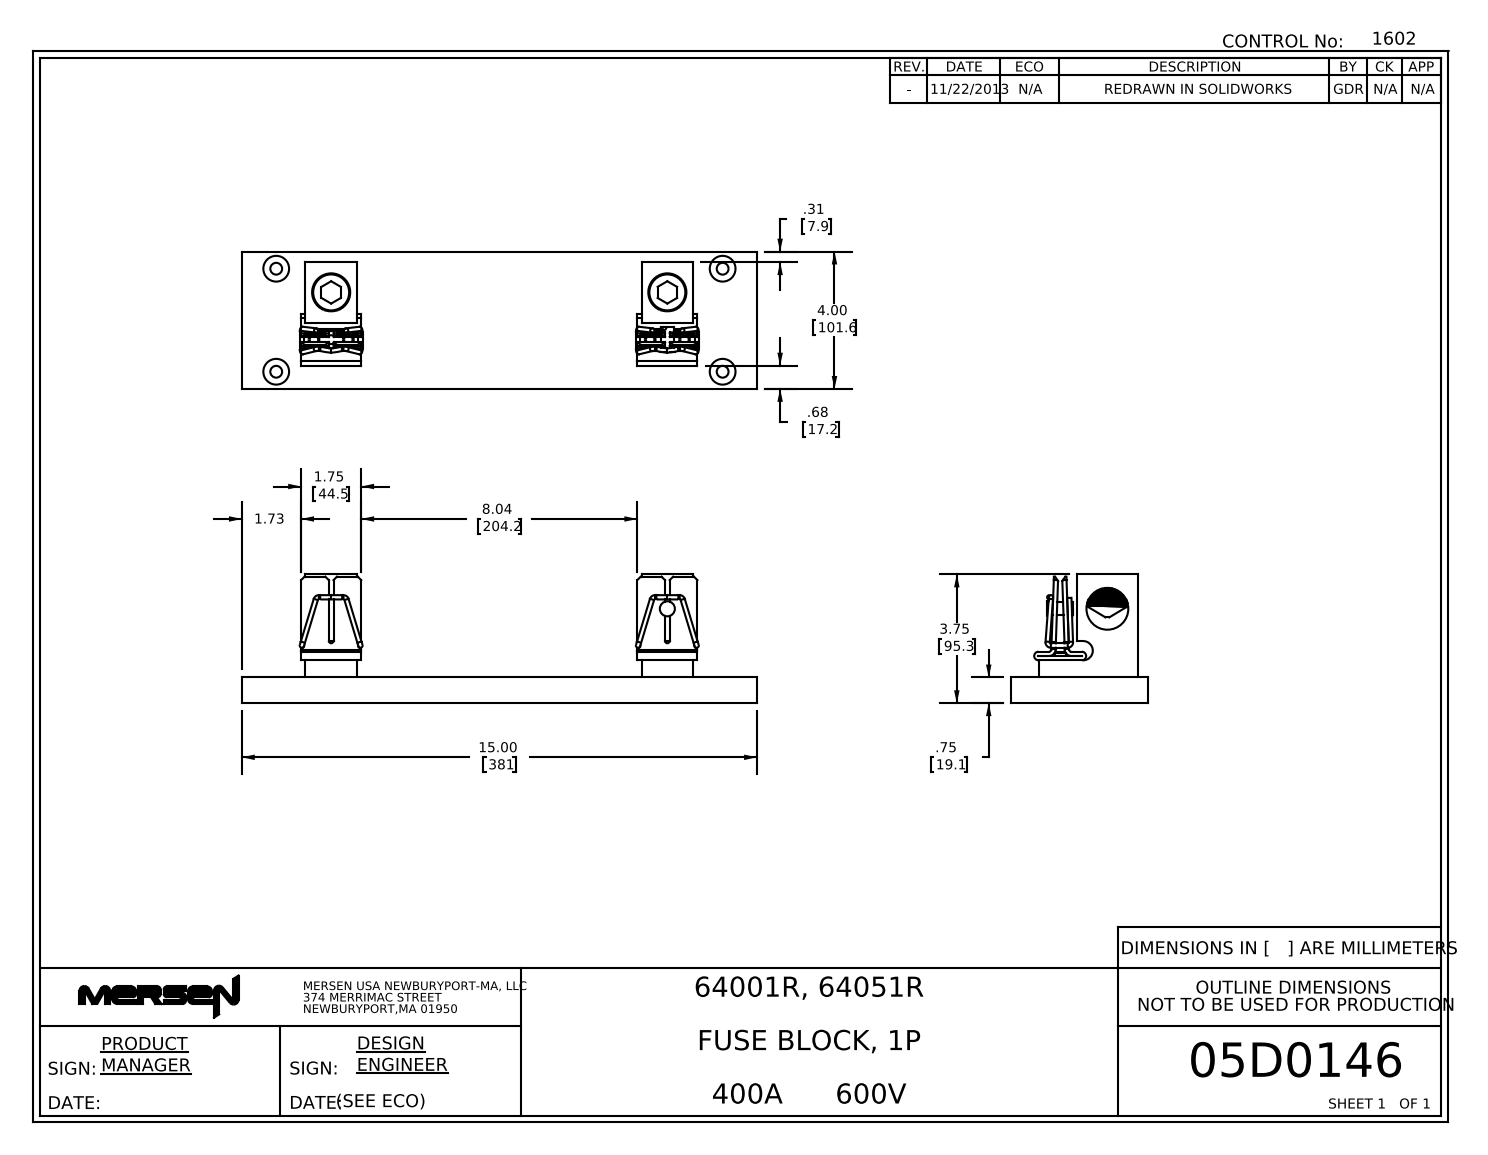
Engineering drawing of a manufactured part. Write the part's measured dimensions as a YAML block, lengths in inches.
part_name: "05D0146rev"
step_written_by: "SolidWorks 2013 (AUTOMOTIVE_DESIGN)"
units: inches
bodies: {solids: 18, faces: 511, planar: 214, cylindrical: 142, other: 155}
overall_size: [15, 4, 3.75]
volume: 60.58
surface_area: 319.6
round_holes:
  - {diameter: 0.257, count: 4}
  - {diameter: 0.266, count: 4}
  - {diameter: 0.339, count: 4}
  - {diameter: 0.344, count: 4}
  - {diameter: 0.377, count: 4}
  - {diameter: 0.625, count: 4}
  - {diameter: 0.75, count: 4}
  - {diameter: 0.85, count: 4}
  - {diameter: 1.047, count: 2}
  - {diameter: 1.218, count: 2}
round_bosses_or_shafts:
  - {diameter: 1.095, count: 28}
  - {diameter: 0.313, count: 8}
  - {diameter: 1.17, count: 2}
  - {diameter: 0.438, count: 1}
  - {diameter: 0.375, count: 1}
partial_cylinders:
  - {radius: 0.094, count: 4}
  - {radius: 0.125, count: 3}
  - {radius: 0.063, count: 2}
  - {radius: 0.069, count: 2}
  - {radius: 0.187, count: 2}
  - {radius: 0.141, count: 1}
  - {radius: 0.195, count: 1}
  - {radius: 0.28, count: 1}
face_to_face_distances: [0.75, 0.124, 0.5, 1.5, 4, 9.79, 0.31, 3.69, 1.25, 0.124]
hole_center_spacings: [9.79, 1, 0.596, 0.599, 1.458, 1.935, 1.936, 1.94]
